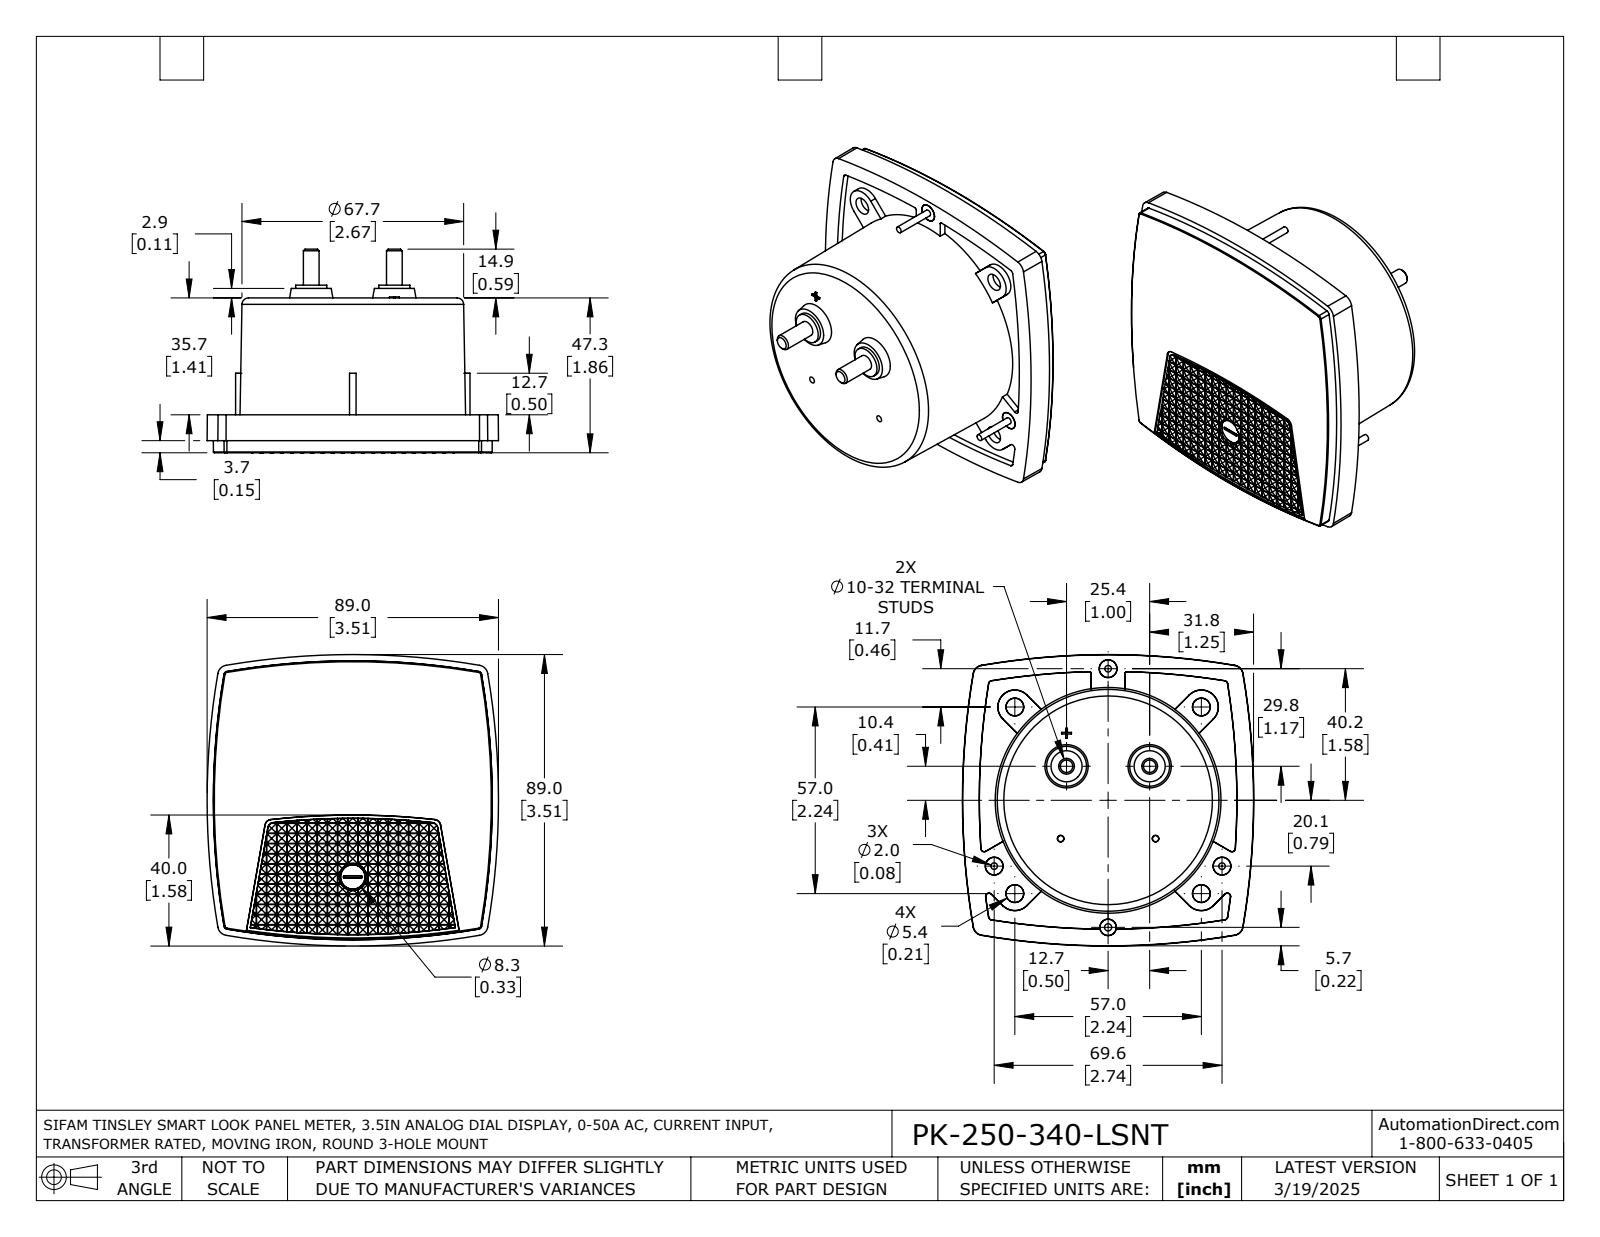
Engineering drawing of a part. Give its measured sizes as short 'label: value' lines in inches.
name: PK-250-340-LSNT
written by: SolidWorks 2021 (AUTOMOTIVE_DESIGN)
unit: in
bodies: 1 solid, 1078 faces (950 planar, 23 cylindrical, 105 other)
size: 3.505 × 3.505 × 2.453
volume: 12.99 in³; area: 44.29 in²
holes: 1× ⌀0.087
bosses: 3× ⌀0.213, 3× ⌀0.079, 2× ⌀0.374, 2× ⌀0.189
rounds: 1× R8.961
face distances: 1.862, 1.406, 0.457, 0.079, 1.484, 0.378, 0.024, 0.096, 0.072, 0.12
